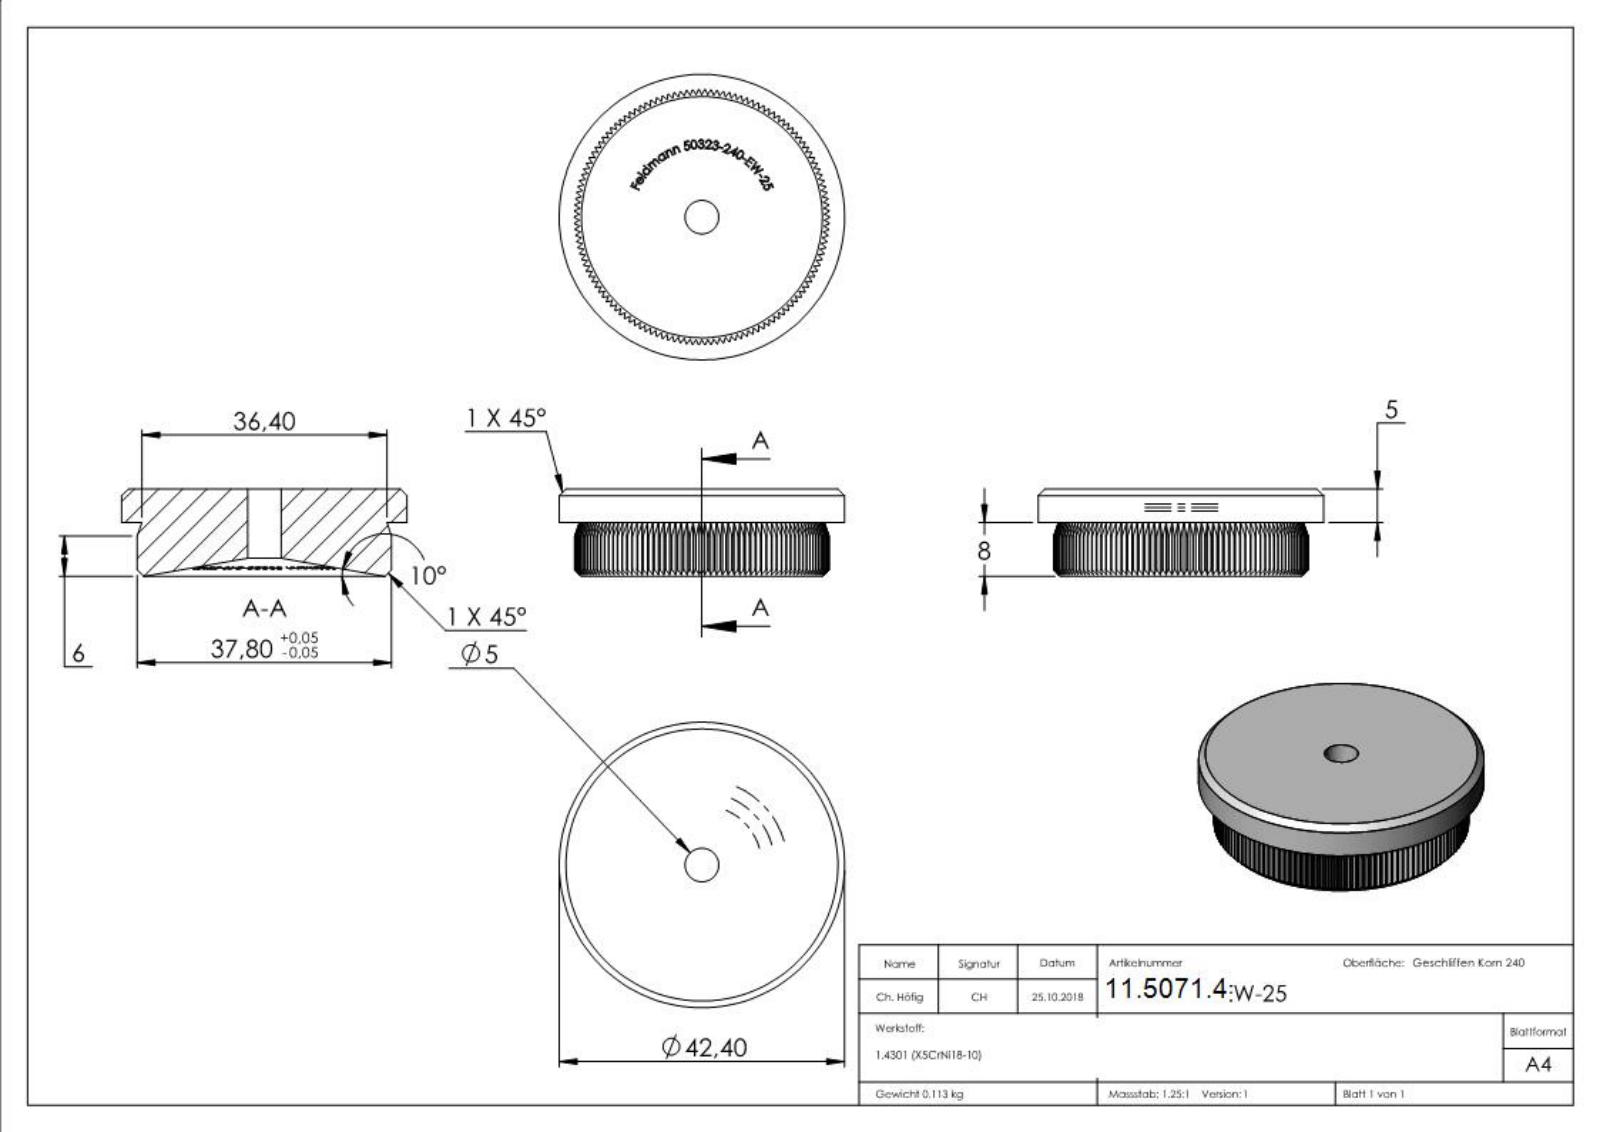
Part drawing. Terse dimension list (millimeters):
name: 50323-240-EW-25
written by: SolidWorks 2015 (CONFIG_CONTROL_DESIGN)
unit: mm
bodies: 1 solid, 826 faces (405 planar, 134 cylindrical, 287 other)
size: 42.4 × 42.4 × 13
volume: 14 356 mm³; area: 5 173 mm²
holes: 1× ⌀5
bosses: 1× ⌀42.4
rounds: 1× R18.9
face distances: 18.2, 5, 18.22, 18.18, 0.72, 0.53, 0.66, 1.32, 0.55, 0.6
